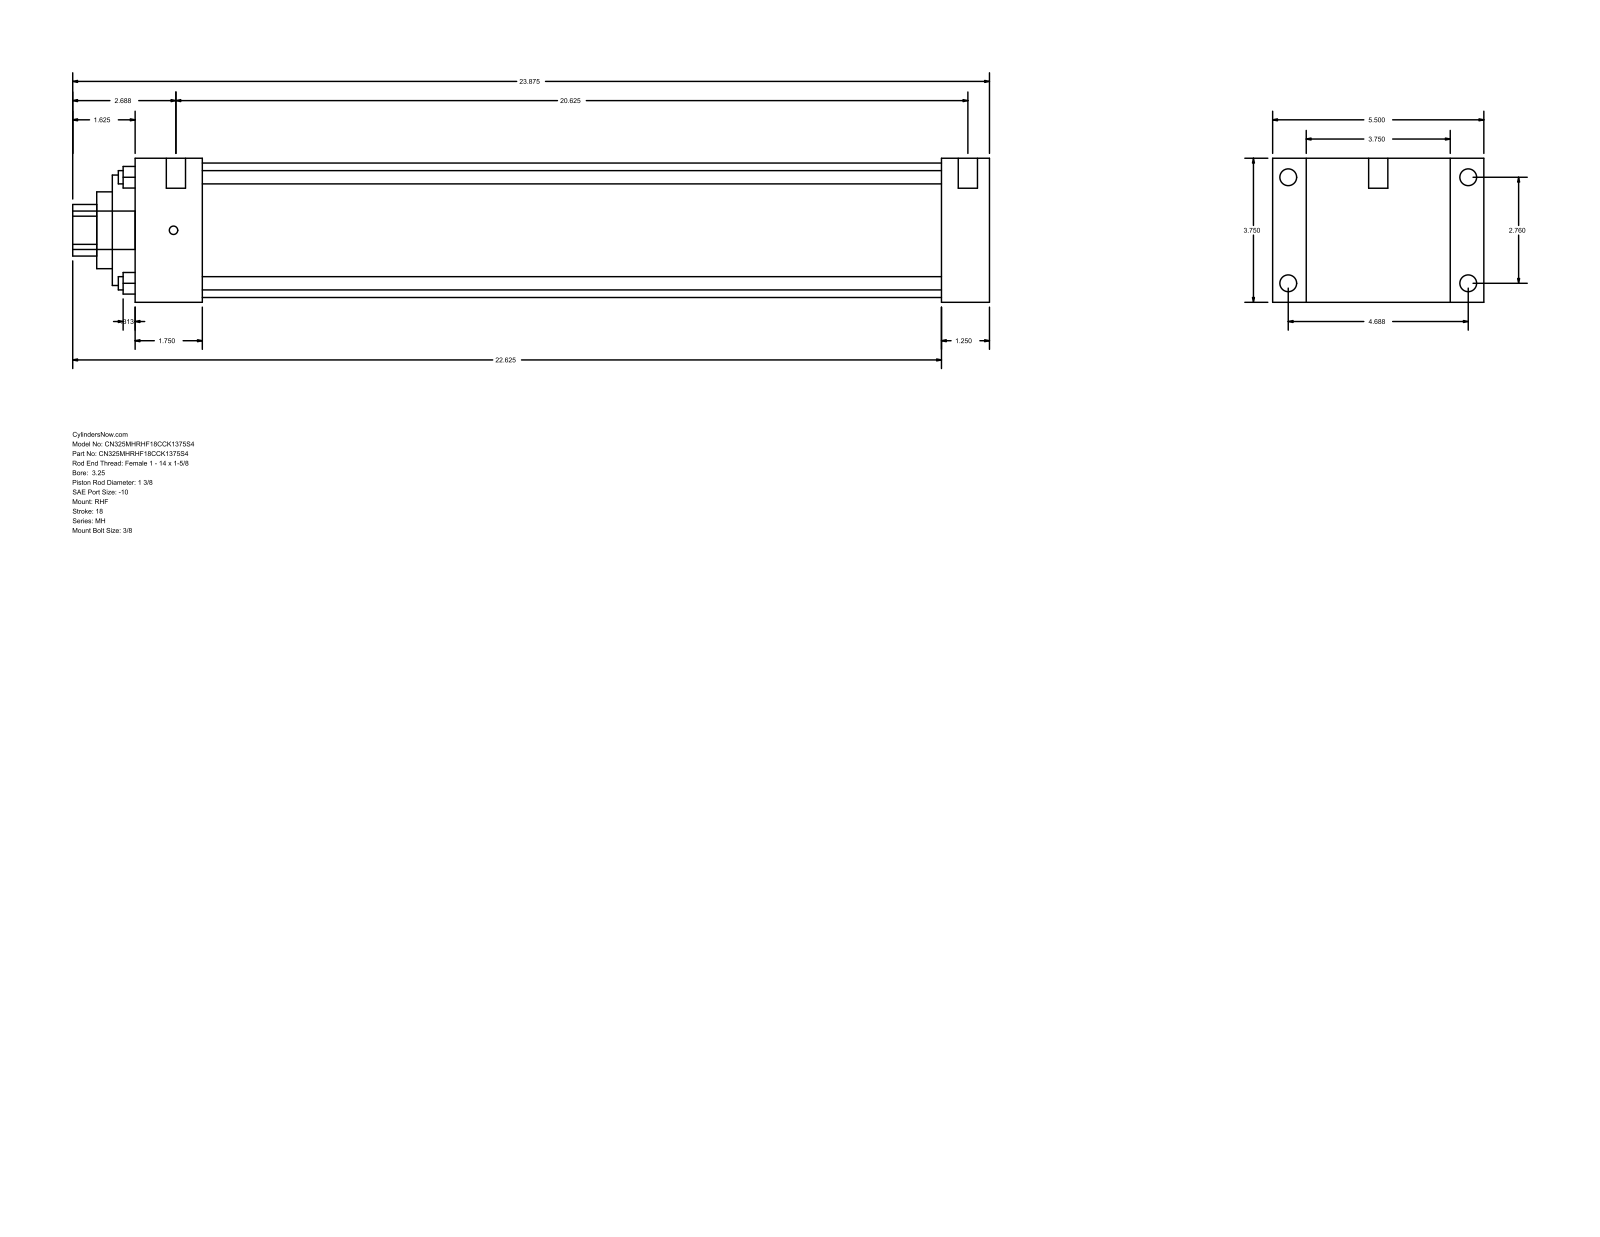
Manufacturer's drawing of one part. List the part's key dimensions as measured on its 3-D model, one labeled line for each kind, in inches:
Part name (STEP PRODUCT): MH_RHF__0325_1.375
STEP written by: GSSL Pune (CONFIG_CONTROL_DESIGN)
Units: inches
Bodies: 0 solids, 90 faces (61 planar, 29 cylindrical, 0 other)
Overall size (bounding box): 23.875 × 5.5 × 3.75
Round holes (diameter × count): ⌀0.345 ×4, ⌀1.375 ×1, ⌀2 ×1, ⌀2.875 ×1, ⌀3.5 ×1
Round bosses / shafts (diameter × count): ⌀0.438 ×4, ⌀0.219 ×4, ⌀0.5 ×2, ⌀1 ×1
Partial cylindrical surfaces — rounded edges, fillets, slot ends (radius × count): R0.672 ×1
Main face-to-face distances: 3.75, 1.25, 0.875, 4.625, 21, 22.25, 5.5, 1.75, 19.25, 20.5
Hole centre spacings: 1.952, 2.76, 3.903
